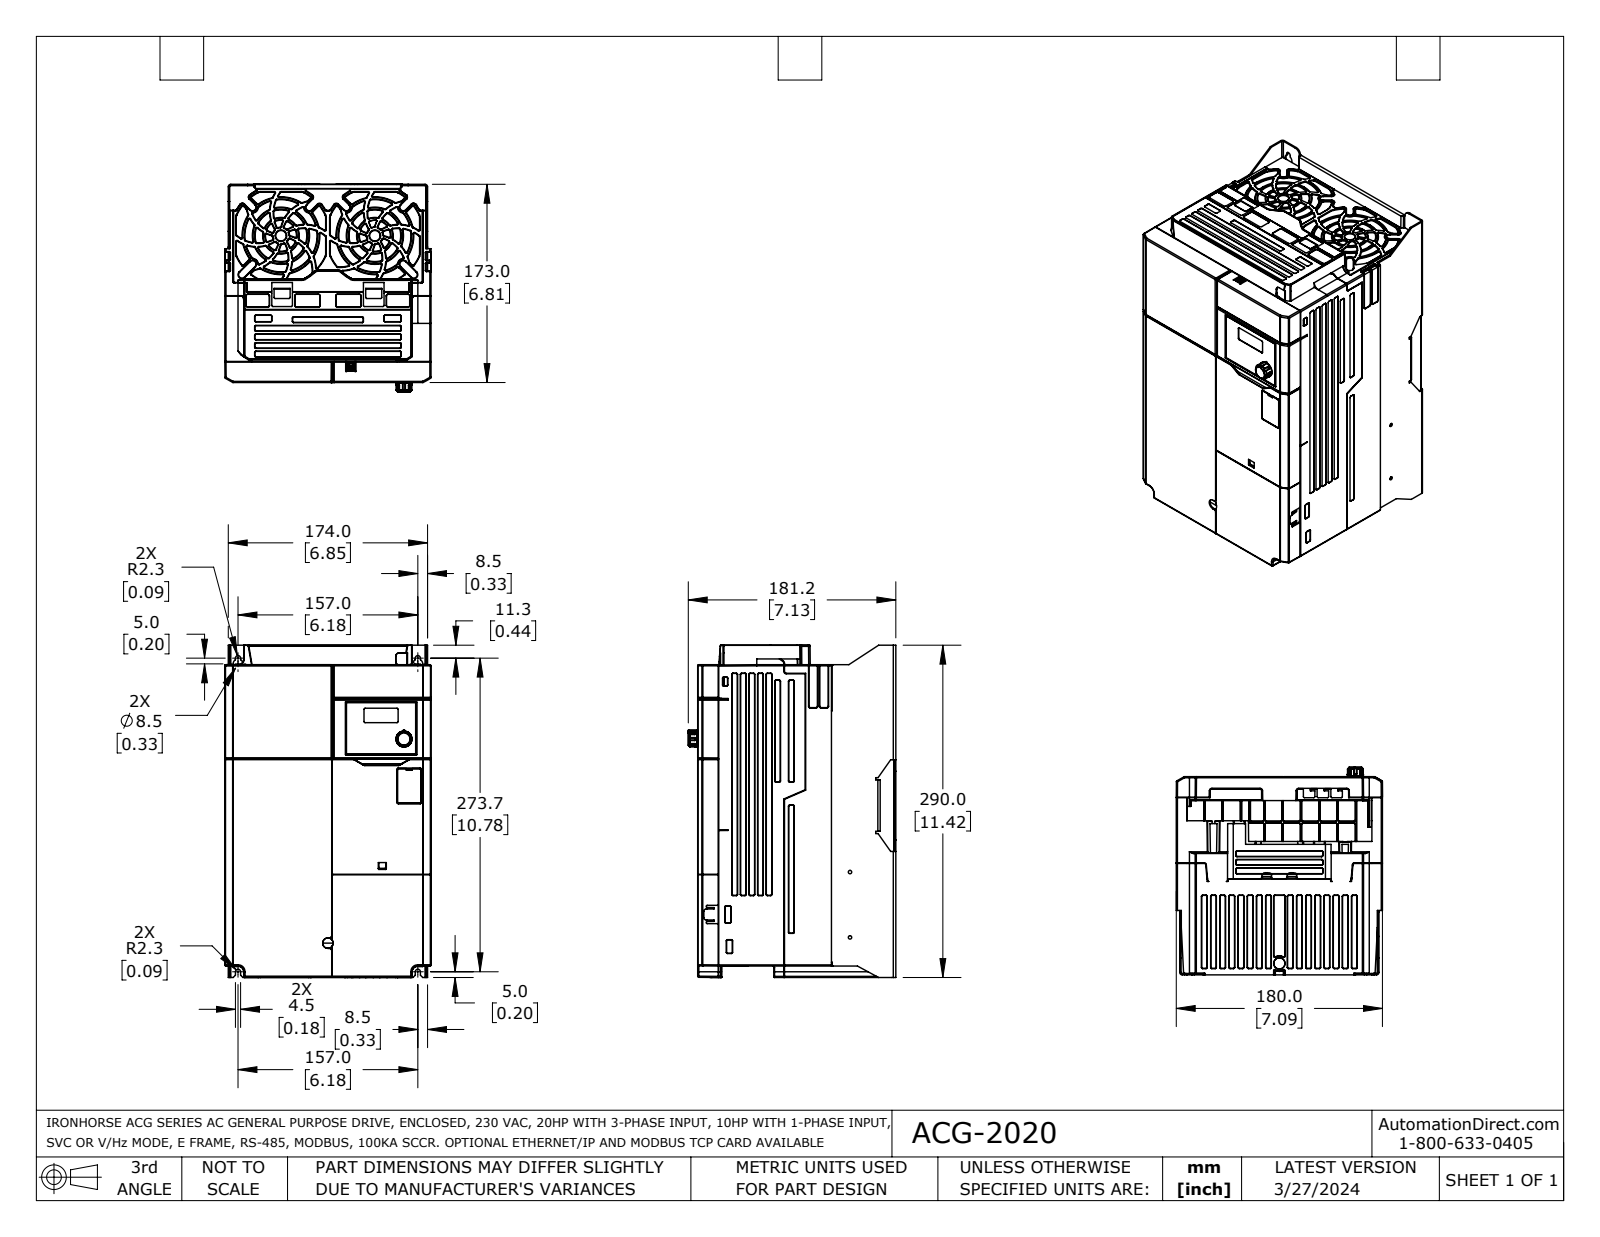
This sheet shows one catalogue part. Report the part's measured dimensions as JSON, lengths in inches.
{"part_name": "ACG-2020", "step_written_by": "SolidWorks 2021 (AUTOMOTIVE_DESIGN)", "units": "inches", "bodies": {"solids": 6, "faces": 3664, "planar": 1665, "cylindrical": 663, "other": 1336}, "overall_size": [11.418, 7.134, 7.087], "volume_in3": 150.2, "surface_area_in2": 855.8, "round_holes": [[0.161, 4], [0.177, 3], [0.217, 3], [0.118, 2], [0.335, 2], [0.039, 1], [0.362, 1], [0.472, 1]], "round_bosses_or_shafts": [[0.386, 2], [0.327, 2], [0.197, 2], [0.551, 1], [0.543, 1], [0.335, 1], [0.315, 1], [0.259, 1]], "partial_cylinders_radius": [[0.039, 124], [0.008, 108], [0.02, 95], [0.012, 36], [0.079, 14], [0.197, 12], [0.087, 9], [0.177, 6]], "face_to_face_distances": [0.055, 6.811, 6.756, 0.453, 6.634, 6.181, 0.118, 6.969, 0.335, 6.516], "hole_center_spacings": [0.433, 0.894, 0.945, 1.378, 1.811, 1.835, 2.267, 2.7]}
